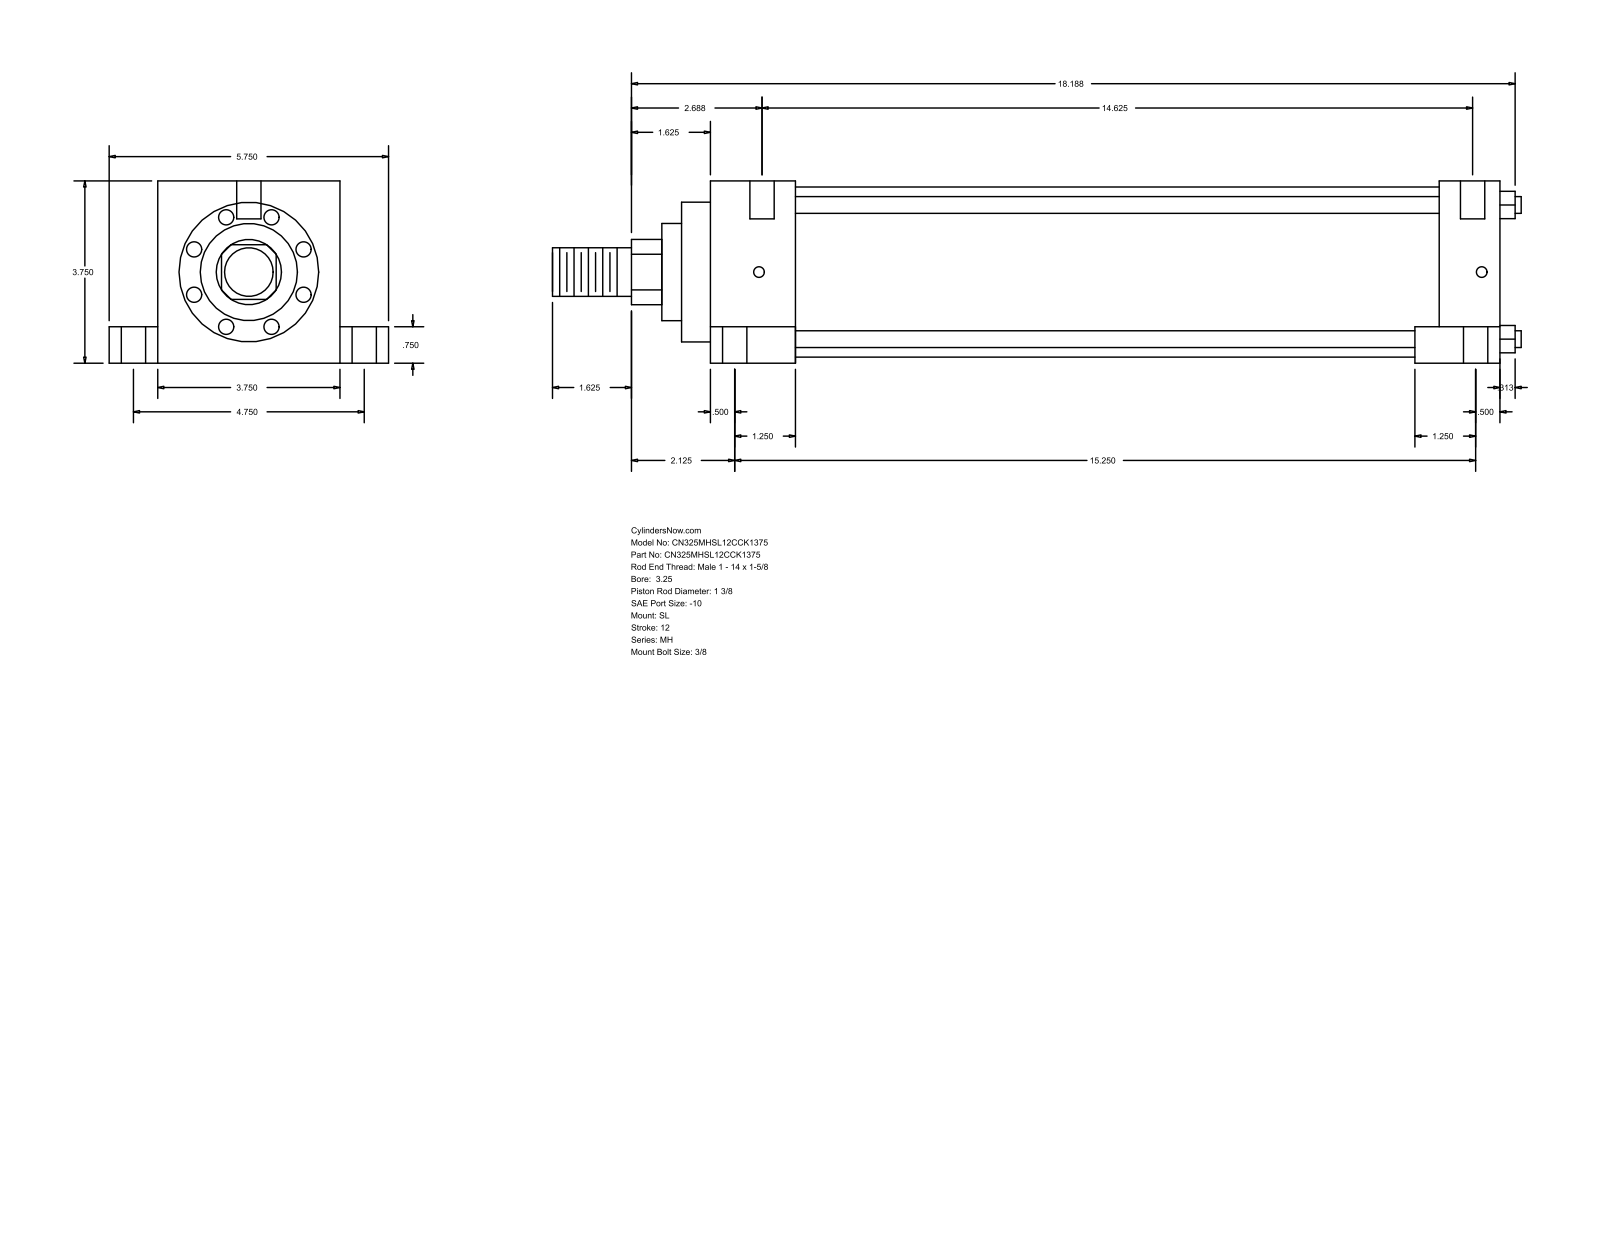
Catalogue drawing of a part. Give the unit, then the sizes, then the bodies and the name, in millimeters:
Units: millimetres
Overall size (bounding box): 506.41 × 146.05 × 95.25
Round holes (diameter × count): ⌀12.7 ×6, ⌀5.56 ×4, ⌀19.05 ×4
Round bosses / shafts (diameter × count): ⌀8.76 ×4, ⌀88.9 ×1, ⌀73.03 ×1, ⌀50.8 ×1, ⌀34.92 ×1, ⌀25.4 ×1
Partial cylindrical surfaces — rounded edges, fillets, slot ends (radius × count): R17.06 ×1
Main face-to-face distances: 95.24, 412.75, 44.45, 368.3, 25.41, 120.65, 19.05, 76.19, 381, 336.55
Hole centre spacings: 60.35, 60.41, 61.65, 62, 120.66, 377.83, 377.91, 379.48
Bodies: 0 solids, 110 faces (77 planar, 33 cylindrical, 0 other)
Part name (STEP PRODUCT): MH_SL__0325_1.375
STEP written by: GSSL Pune (CONFIG_CONTROL_DESIGN)
